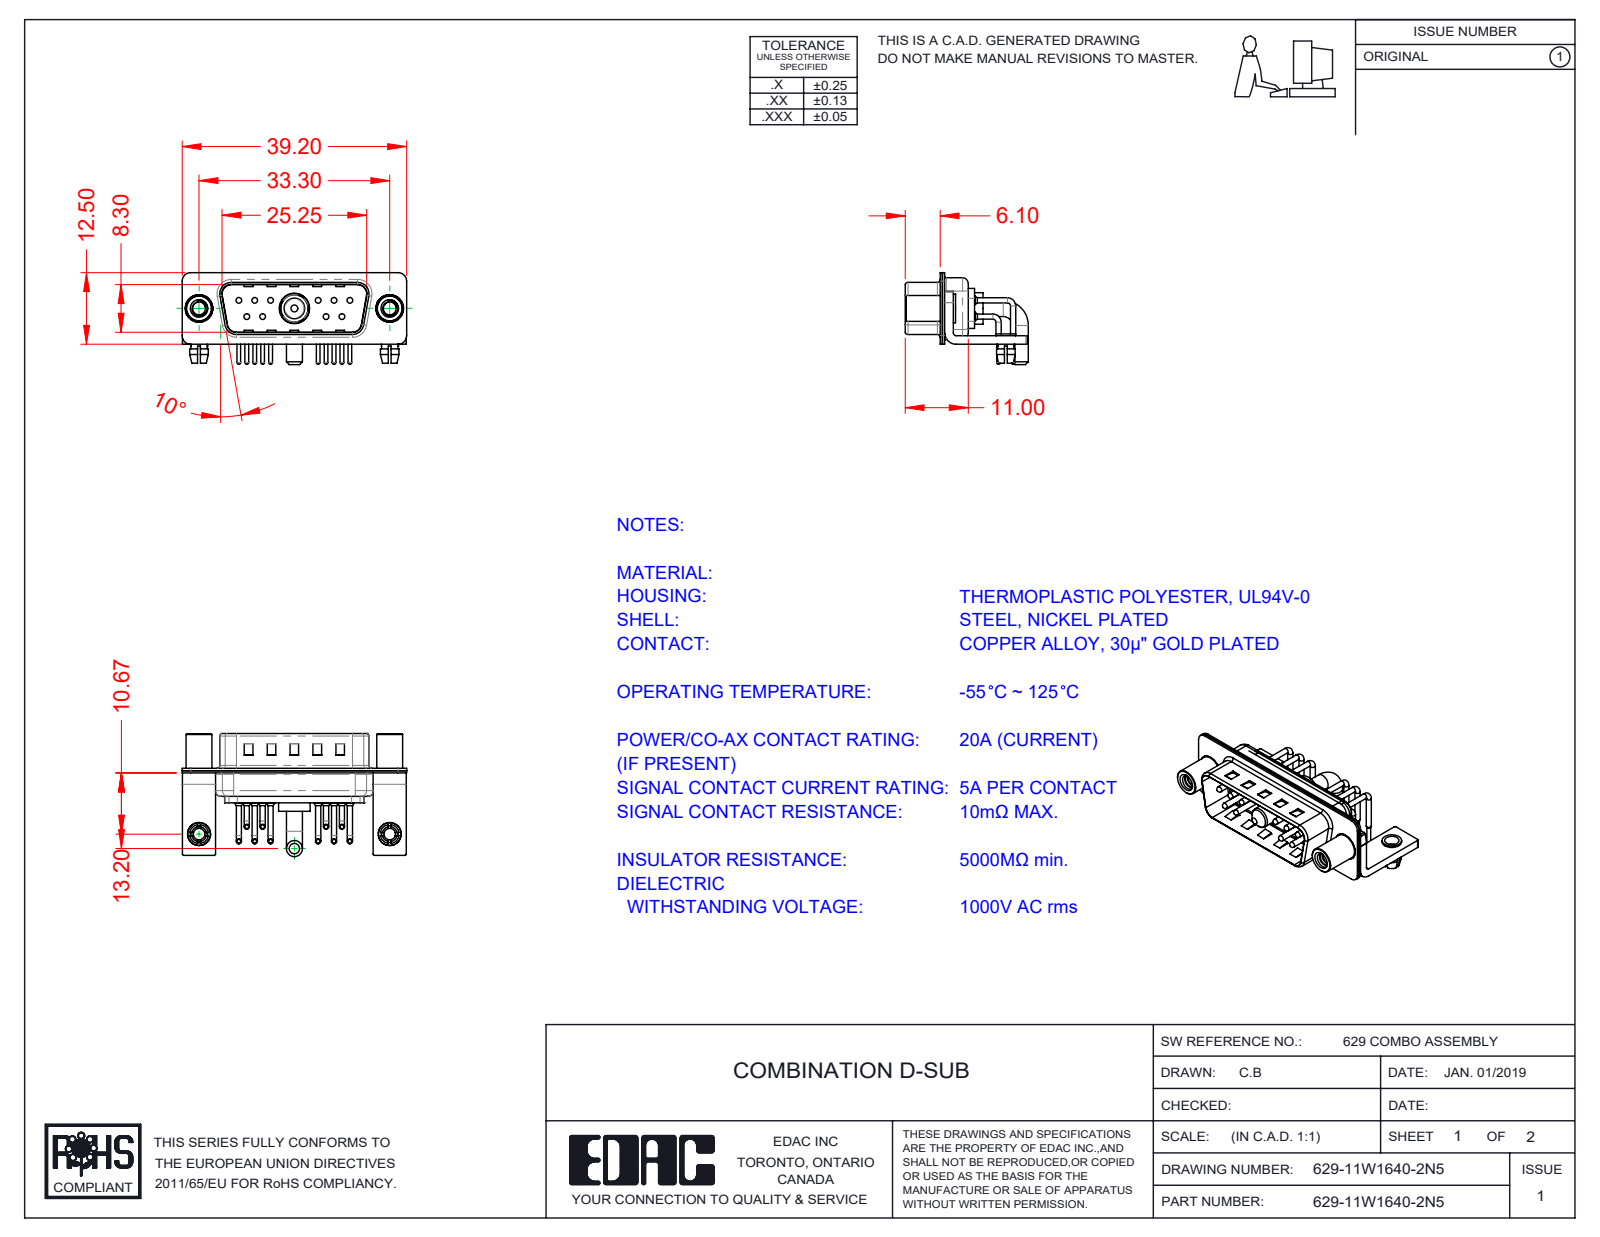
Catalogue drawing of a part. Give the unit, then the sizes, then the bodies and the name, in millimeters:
Units: millimetres
Overall size (bounding box): 39.2 × 21.5 × 16.05
Round holes (diameter × count): ⌀2 ×12, ⌀0.75 ×10, ⌀1.6 ×10, ⌀2.26 ×2, ⌀2.5 ×2, ⌀3.2 ×2, ⌀4 ×2, ⌀4.8 ×2, ⌀4.85 ×1, ⌀5.3 ×1
Round bosses / shafts (diameter × count): ⌀0.9 ×20, ⌀1.5 ×10, ⌀1 ×10, ⌀0.65 ×10, ⌀5 ×2, ⌀4.9 ×2, ⌀4.5 ×2, ⌀4 ×2
Partial cylindrical surfaces — rounded edges, fillets, slot ends (radius × count): R0.25 ×16, R1.5 ×16, R2 ×13, R1.01 ×10, R0.5 ×9, R1.6 ×8, R1 ×7, R0.6 ×4
Main face-to-face distances: 0.4, 0.8, 1.5, 9.5, 9.1, 8.7, 9.9, 0.6, 1.9, 0.75
Hole centre spacings: 3.16, 2.77, 13.85, 11.08, 16.62, 5.03, 5.04, 5.54
Volume: 2 496 mm³ · Surface area: 6 358 mm²
Bodies: 21 solids, 1676 faces (868 planar, 610 cylindrical, 198 other)
Part name (STEP PRODUCT): 629Combo Threaded Standoff_5; 629Combo Contact Row 2; 629-11W1640-2N5; 629Combo Shell Front_15 Contacts (+6 more)
STEP written by: SolidWorks 2020 (CONFIG_CONTROL_DESIGN)
